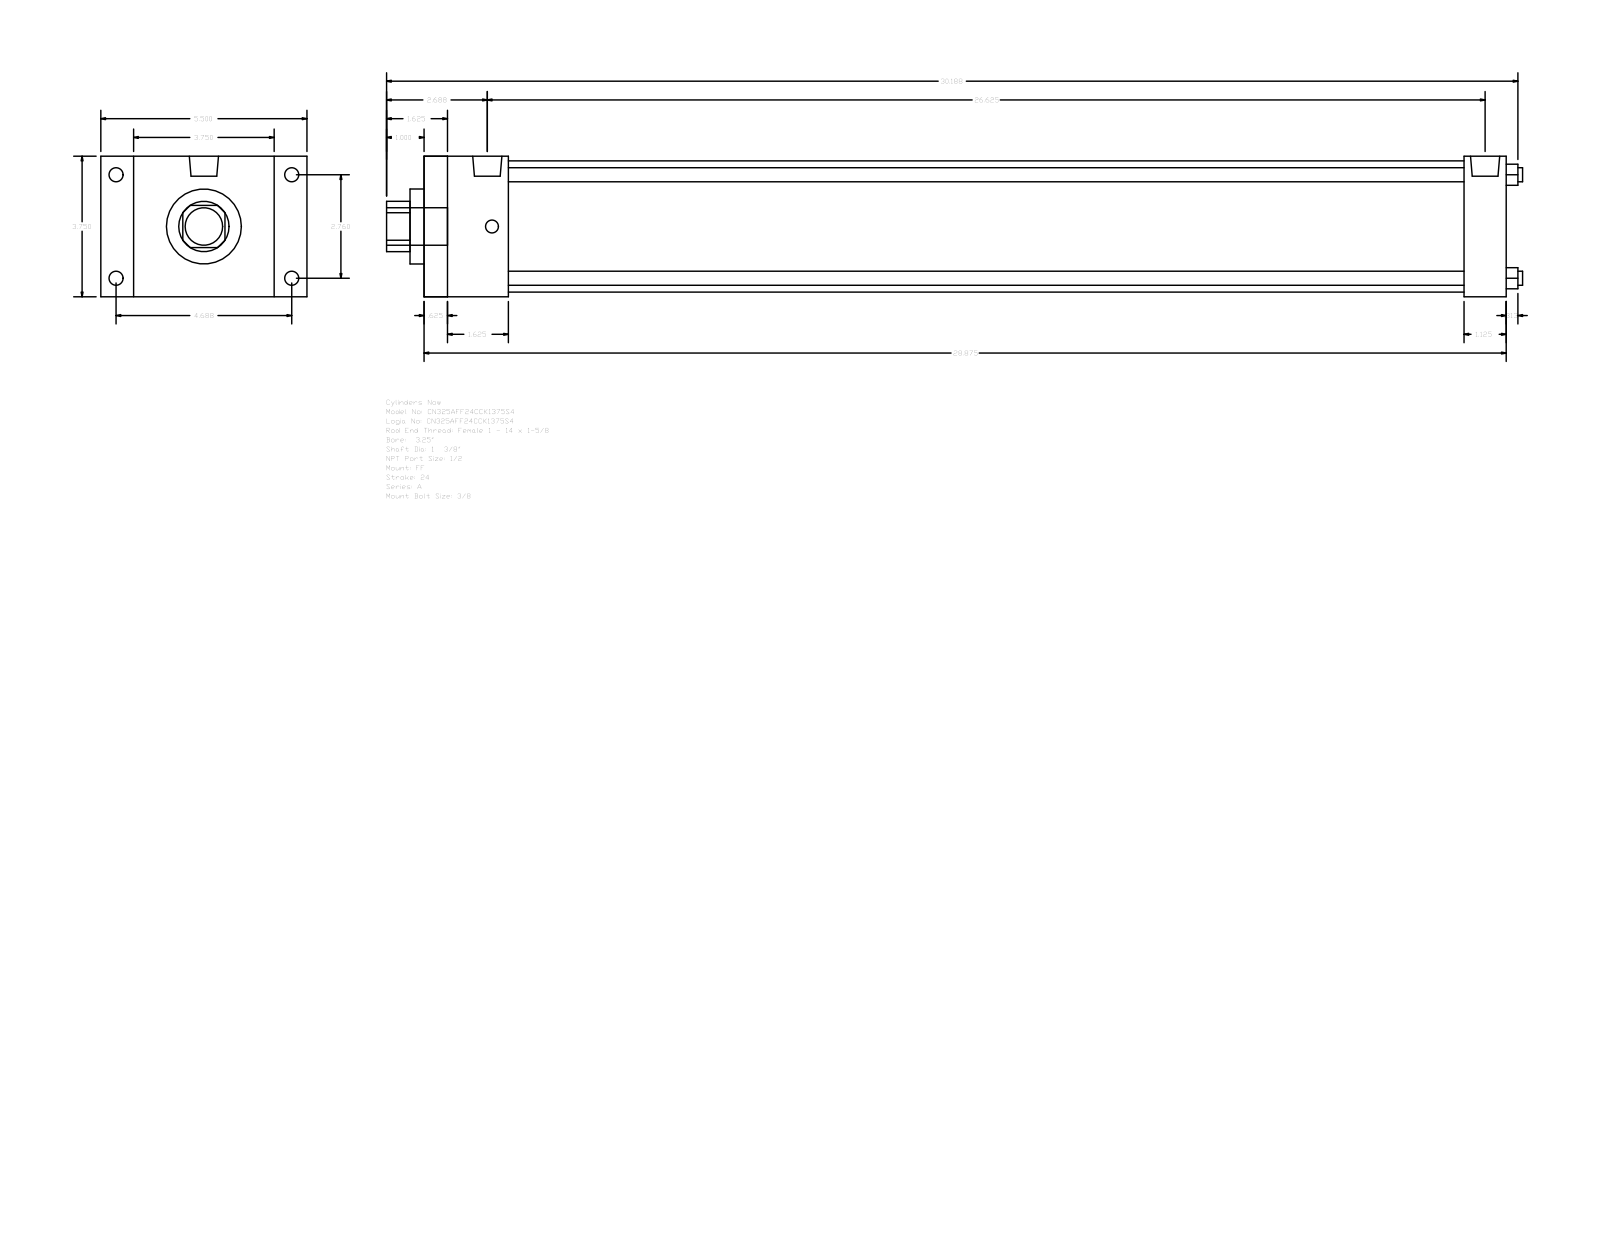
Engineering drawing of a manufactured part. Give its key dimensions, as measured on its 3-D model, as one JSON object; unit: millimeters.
{"part_name": "A_FF__0325_1.375", "step_written_by": "GSSL Pune (CONFIG_CONTROL_DESIGN)", "units": "millimeters", "bodies": {"solids": 0, "faces": 92, "planar": 64, "cylindrical": 28, "other": 0}, "overall_size": [769.94, 139.7, 95.25], "round_holes": [[9.53, 4], [34.92, 1], [50.8, 1], [88.9, 1]], "round_bosses_or_shafts": [[9.53, 4], [8.73, 4], [19.77, 2], [25.4, 1]], "partial_cylinders_radius": [[17.06, 1]], "face_to_face_distances": [95.24, 733.43, 15.87, 717.56, 28.58, 22.23, 117.47, 57.15, 704.85, 41.28], "hole_center_spacings": [49.57, 70.1, 99.14]}
